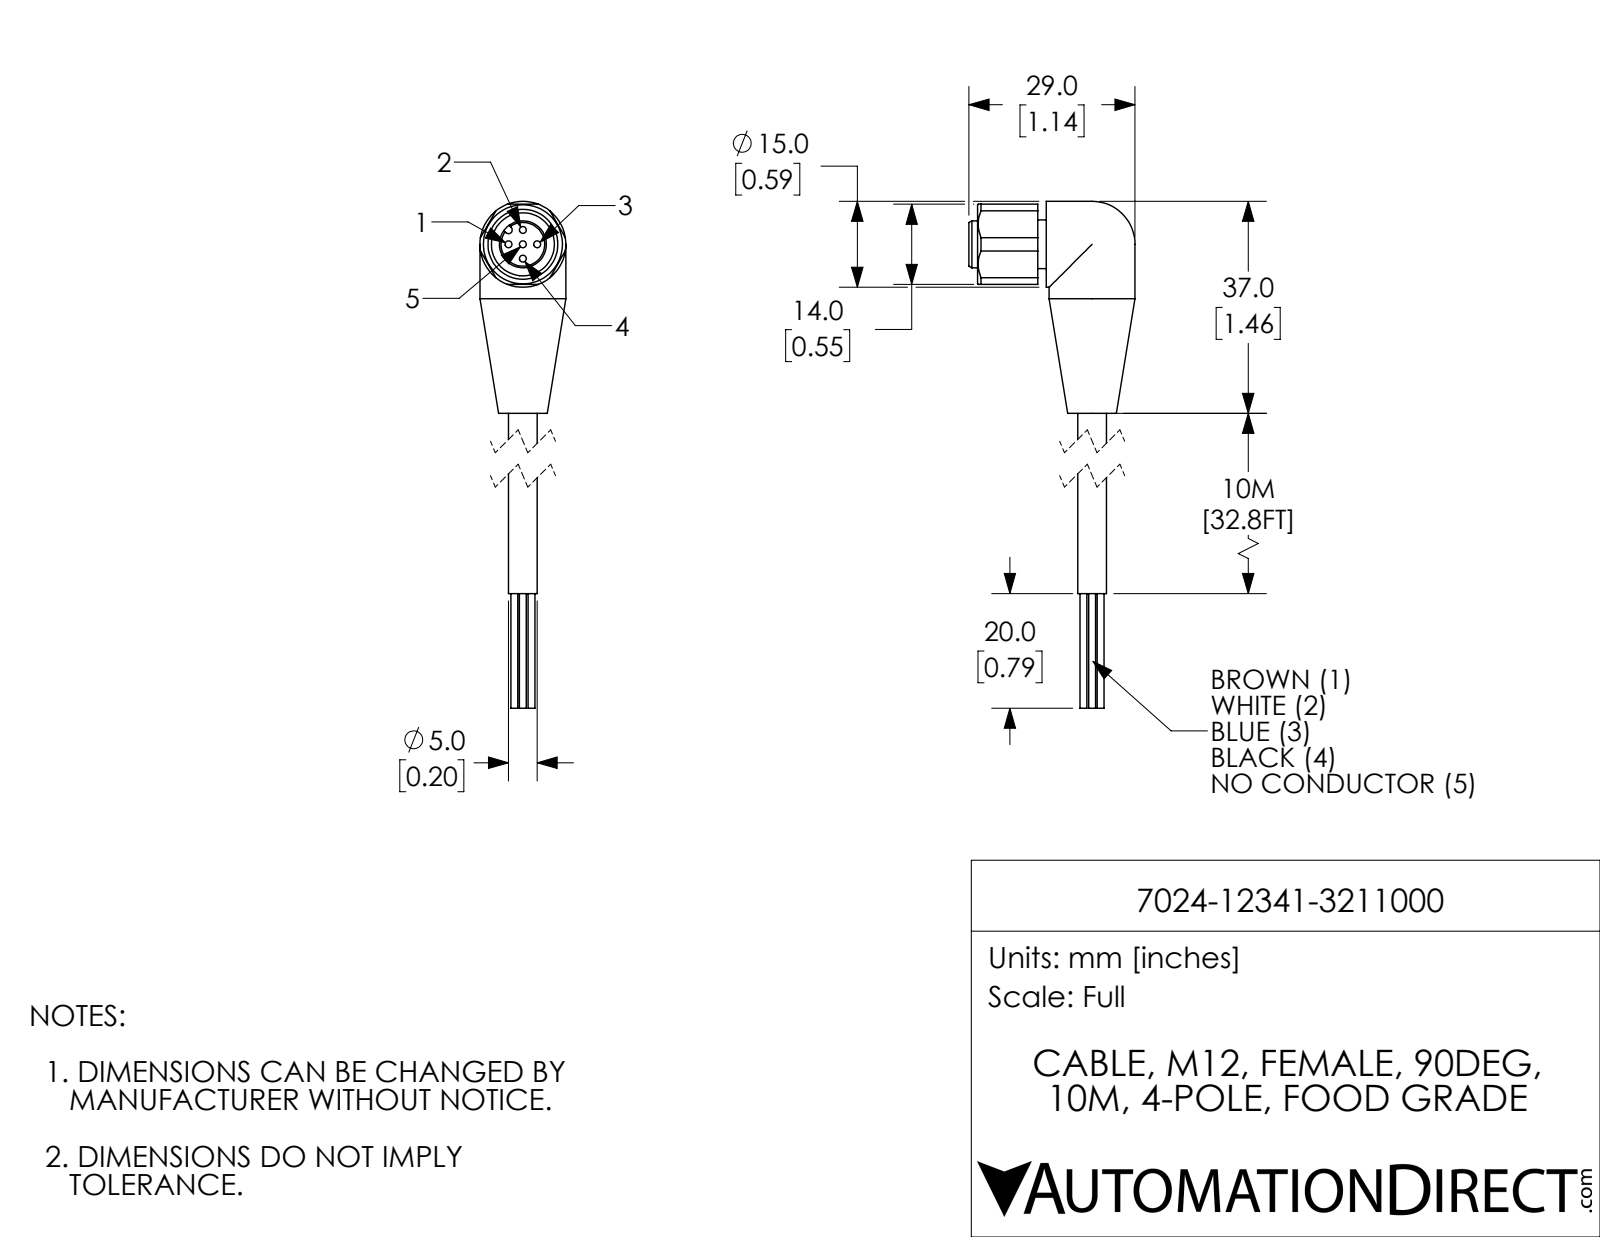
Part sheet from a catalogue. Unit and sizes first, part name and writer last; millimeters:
Units: millimetres
Overall size (bounding box): 87 × 29 × 15
Round holes (diameter × count): ⌀1.2 ×5, ⌀11 ×1
Round bosses / shafts (diameter × count): ⌀1.2 ×4, ⌀15 ×2, ⌀8.5 ×1, ⌀8.2 ×1, ⌀5 ×1
Partial cylindrical surfaces — rounded edges, fillets, slot ends (radius × count): R0.65 ×1
Main face-to-face distances: 14, 1.5, 12, 4.5, 3, 13.5, 9, 22.5, 36.5, 10.5
Hole centre spacings: 2.5, 3.54, 5
Volume: 7 402 mm³ · Surface area: 3 886 mm²
Bodies: 1 solid, 73 faces (25 planar, 38 cylindrical, 10 other)
Part name (STEP PRODUCT): 7024-12341-3211000
STEP written by: SolidWorks 2018 (AUTOMOTIVE_DESIGN)
